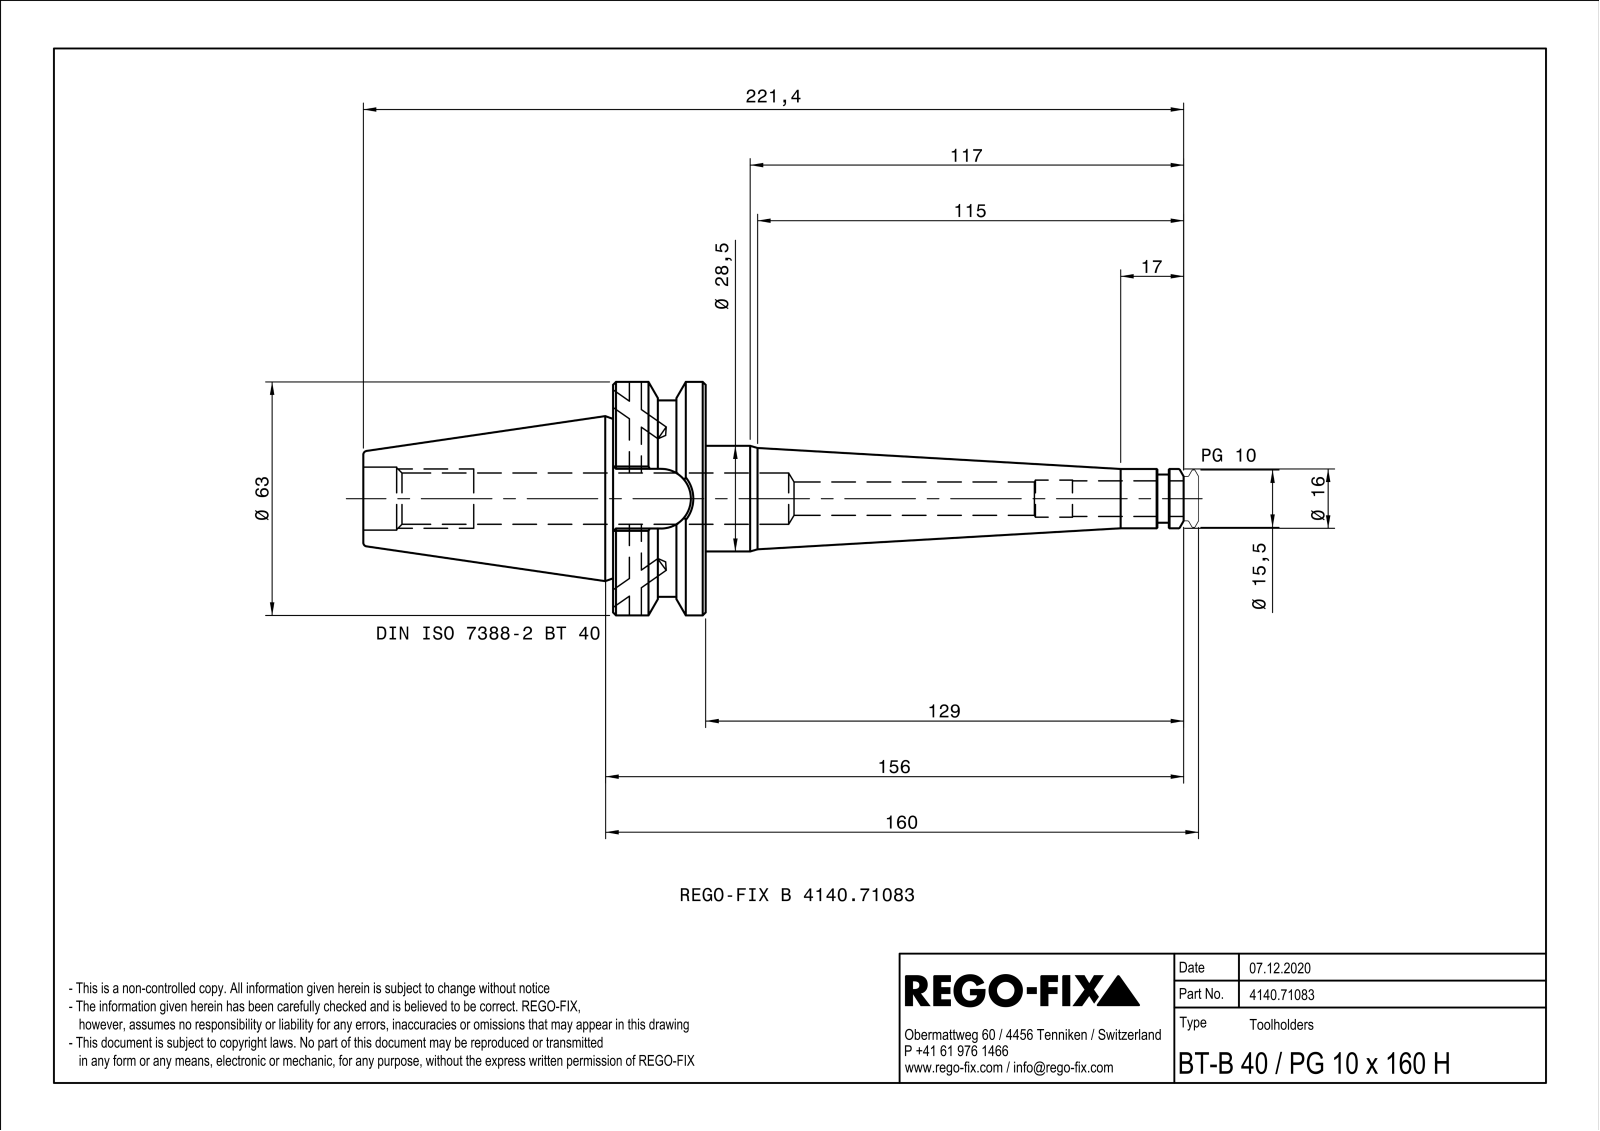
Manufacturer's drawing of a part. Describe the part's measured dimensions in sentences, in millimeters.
The part is named "NOCUT". Its 3-D file was written by "SIEMENS PLM Software Solid Edge ST10 (AUTOMOTIVE_DESIGN)". It is 1 solid with 114 faces: 39 planar, 30 cylindrical and 45 other. Overall it measures 221.4 by 63 by 63 millimeters. Its volume is 155 353 cubic millimeters and its surface area 35 549 square millimeters. Round holes: 2 of diameter 3.24, 2 of diameter 3.9, 1 of diameter 9, 1 of diameter 10, 1 of diameter 13.84, 1 of diameter 17. Round bosses or shafts: 1 of diameter 63, 1 of diameter 53, 1 of diameter 28.5, 1 of diameter 16, 1 of diameter 13. Partial cylindrical surfaces (rounded edges, fillets, slot ends): 4 of radius 0.5, 1 of radius 8.05. The main face-to-face distances are 25, 45.1, 92.4, 67.4, 16.1, 3.1, 125, 150, 217.4, 121.9.
